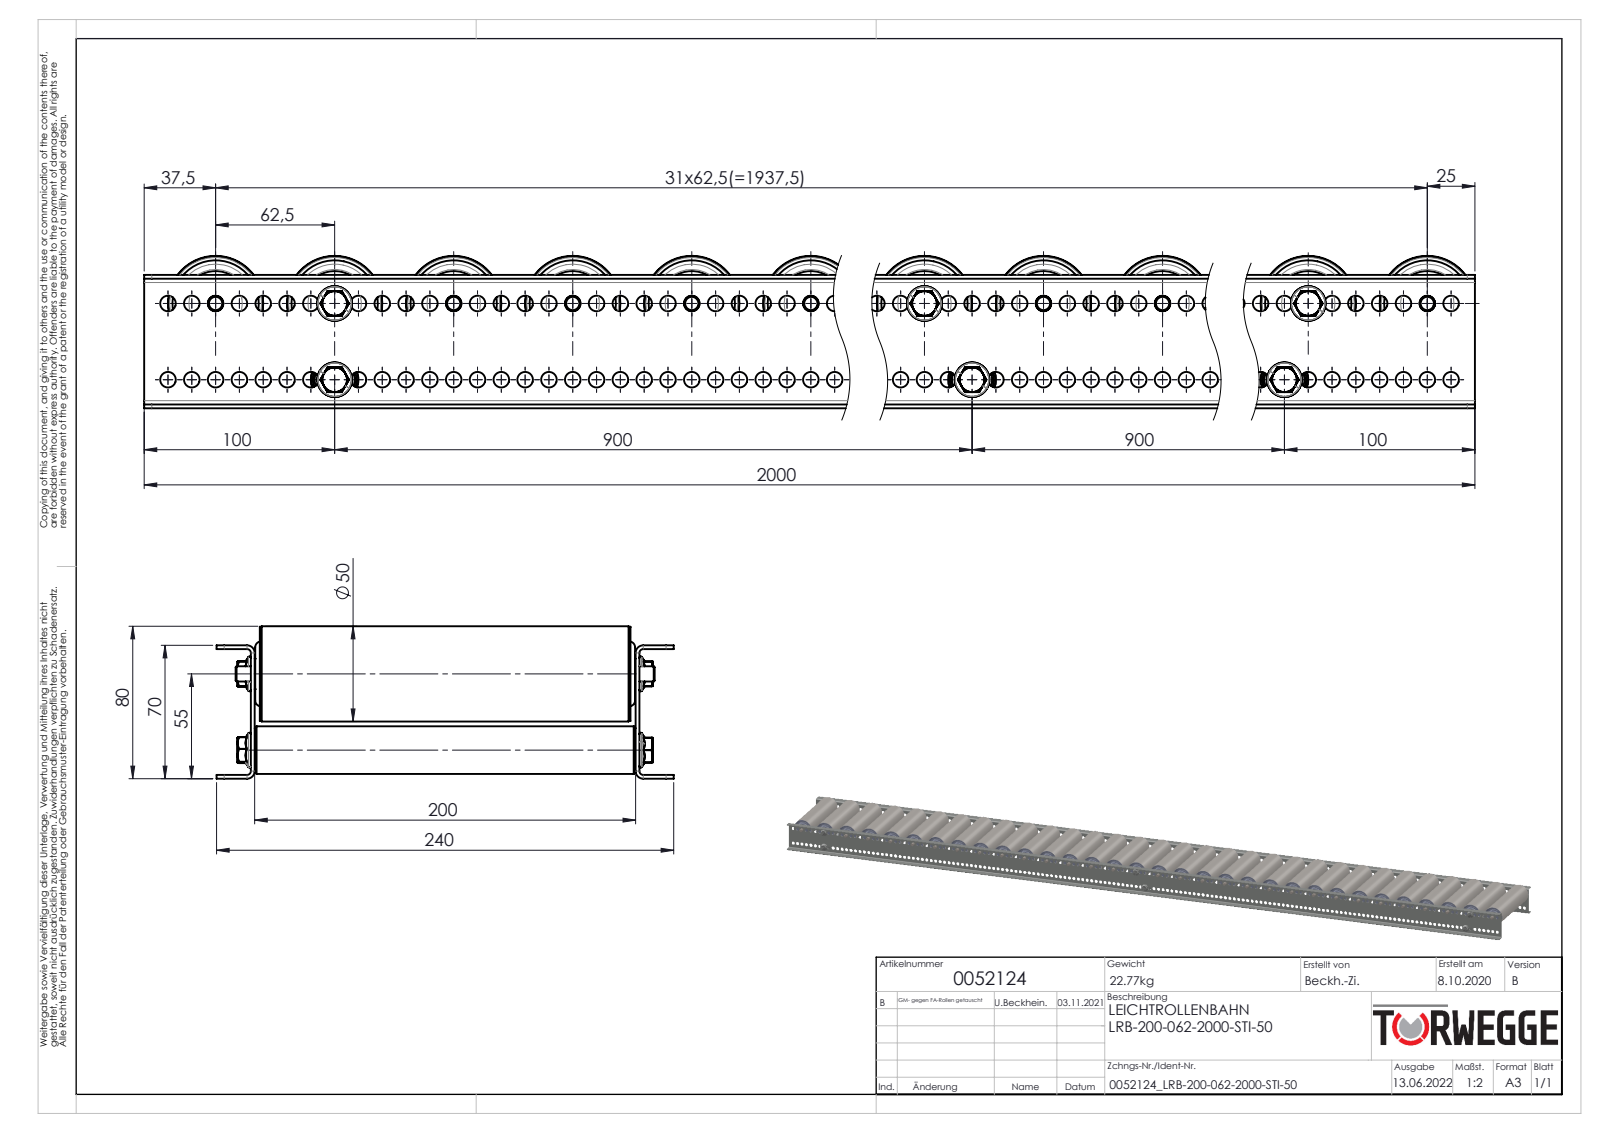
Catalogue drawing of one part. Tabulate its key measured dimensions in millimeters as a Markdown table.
| quantity | value |
| --- | --- |
| part name | 0026295_Typ-TRG_50x1,5-8; TRG-50x1,5-STI-A12-IGM8-EL=KFG_0022776TWG_TRG-50x1,5-STI-A12-IGM8-EL=200; 0024178_Passscheibe_DIN988_12x18x1; Traversen_KFG_L200 (+8 more) |
| STEP written by | SolidWorks 2020 (AUTOMOTIVE_DESIGN) |
| units | millimeters |
| bodies | 728 solids, 12550 faces (2508 planar, 4480 cylindrical, 5562 other) |
| overall size | 2000 × 240 × 80 |
| volume | 3 248 000 mm³ |
| surface area | 3 906 000 mm² |
| round holes (diameter × count) | 8.2 × 318, 17.1 × 32, 18.5 × 32, 27.7 × 32, 45.3 × 32, 47 × 32, 7.6 × 29, 6.8 × 6, 12 × 3, 12.2 × 3, 19.2 × 3, 21 × 3 |
| round bosses / shafts (diameter × count) | 8 × 35, 50 × 32, 49.5 × 32, 47.3 × 32, 29.7 × 32, 27.4 × 32, 27.3 × 32, 16 × 32 |
| partial cylindrical surfaces (radius × count) | 0.6 × 58, 0.75 × 58, 2.45 × 58, 4.87 × 29, 7 × 29, 2.5 × 12, 4 × 8, 2 × 4 |
| main face-to-face distances | 2, 202, 68, 200, 204, 70, 66, 1, 2.3, 201.7 |
| hole center spacings | 12.5, 25, 37.5, 50, 62.5, 75, 87.5, 100 |
